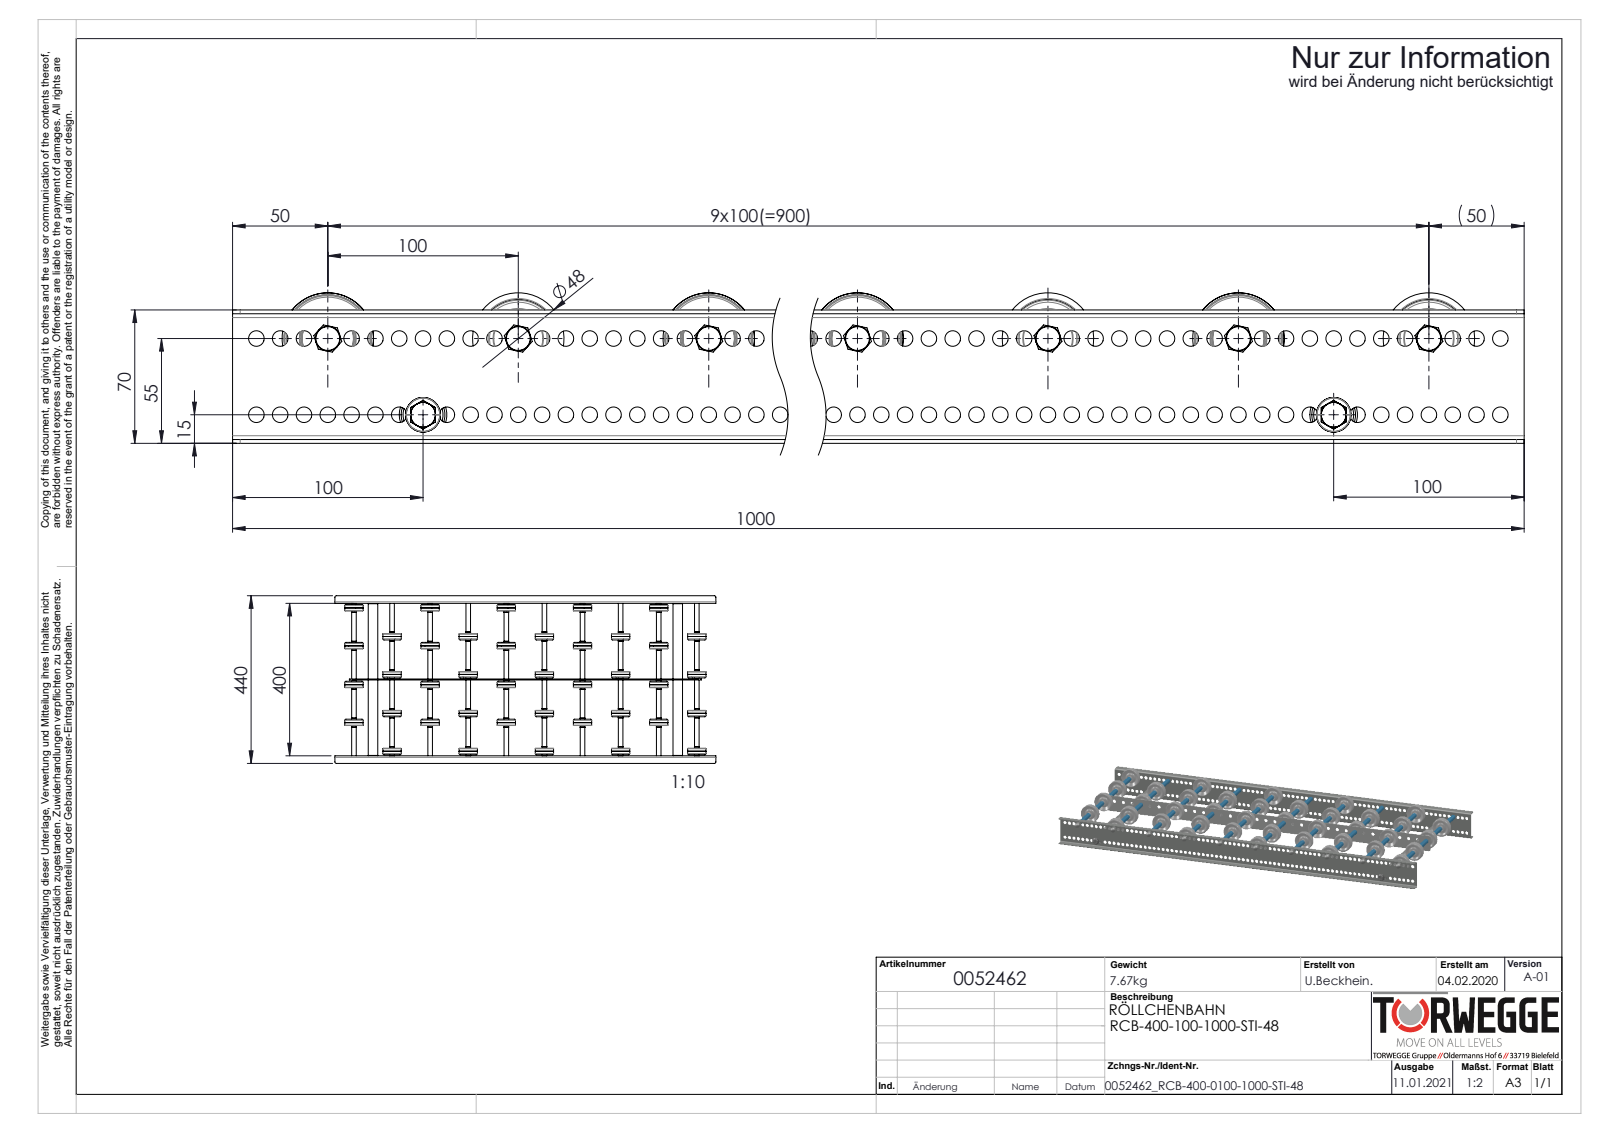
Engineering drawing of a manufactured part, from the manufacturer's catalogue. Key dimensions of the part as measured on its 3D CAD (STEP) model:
Part name (STEP PRODUCT): Traversen_KFG_L400; S100100_Längstraverse-42x2,5_S100101_Lngstraverse-RB-L975; 0052462; Hutmutter_DIN_1587_M8 (+6 more)
STEP written by: SolidWorks 2020 (AUTOMOTIVE_DESIGN)
Units: millimetres
Bodies: 163 solids, 5076 faces (1026 planar, 2066 cylindrical, 1984 other)
Overall size (bounding box): 1000 × 440 × 79
Volume: 1 807 000 mm³ · Surface area: 1 437 000 mm²
Round holes (diameter × count): ⌀8.2 ×158, ⌀8.5 ×37, ⌀6.65 ×10, ⌀8 ×10, ⌀9.65 ×10, ⌀15 ×10, ⌀41 ×10, ⌀6.8 ×2, ⌀21 ×2
Round bosses / shafts (diameter × count): ⌀48 ×10, ⌀13 ×10, ⌀12.5 ×10, ⌀12.4 ×10, ⌀12 ×10, ⌀11.5 ×10, ⌀25 ×2, ⌀8 ×2
Partial cylindrical surfaces — rounded edges, fillets, slot ends (radius × count): R4 ×8, R2 ×4, R5 ×4
Main face-to-face distances: 2, 402, 201.5, 201, 99.5, 75, 68, 404, 400, 111.5
Hole centre spacings: 12.5, 25, 37.5, 50, 62.5, 75, 87.5, 100
